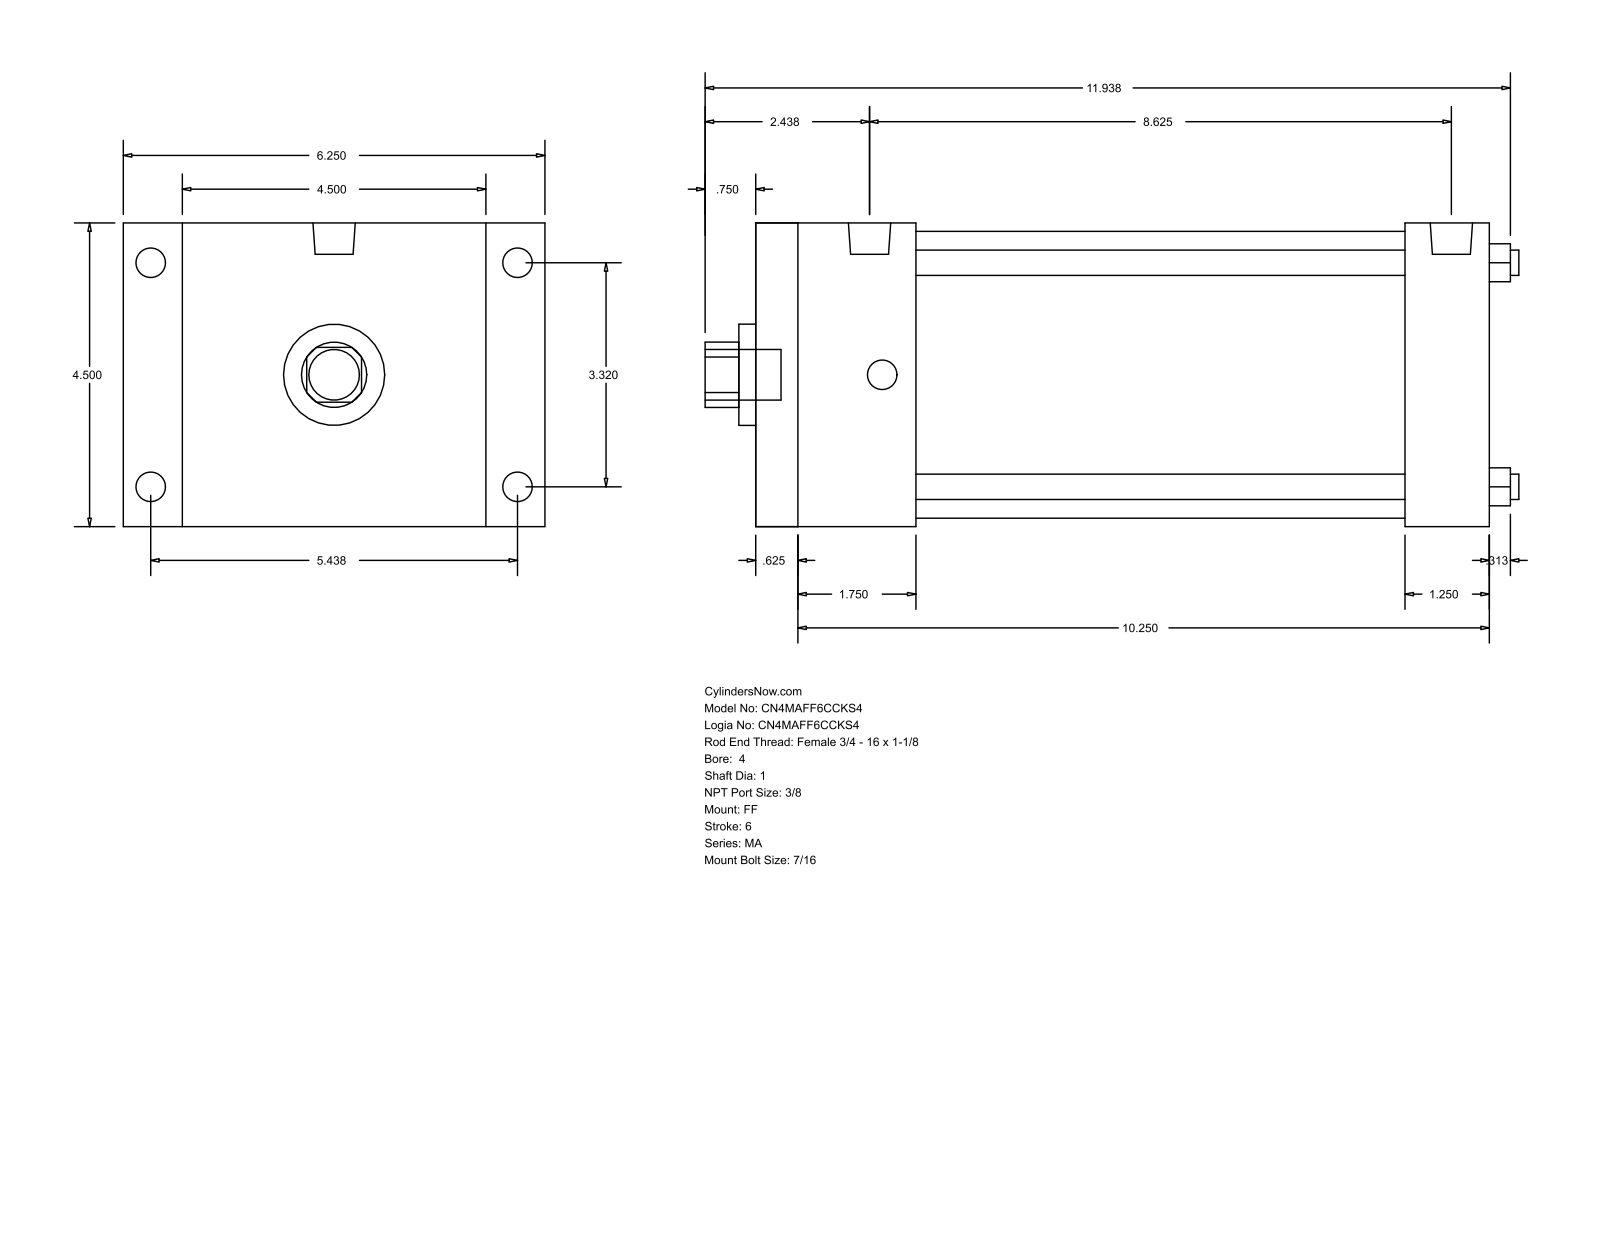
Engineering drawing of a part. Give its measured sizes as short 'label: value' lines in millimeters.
name: MA_FF__0400_1
written by: GSSL Pune (CONFIG_CONTROL_DESIGN)
unit: mm
bodies: 0 solids, 92 faces (64 planar, 28 cylindrical, 0 other)
size: 306.39 × 158.75 × 114.3
holes: 4× ⌀9.53, 1× ⌀25.4, 1× ⌀38.1, 1× ⌀107.95
bosses: 8× ⌀11.11, 2× ⌀15.93, 1× ⌀19.05
rounds: 1× R12.29
face distances: 114.3, 276.22, 15.87, 260.35, 22.23, 136.53, 244.47, 228.6, 31.75, 60.33
hole spacings: 59.62, 84.32, 119.25
